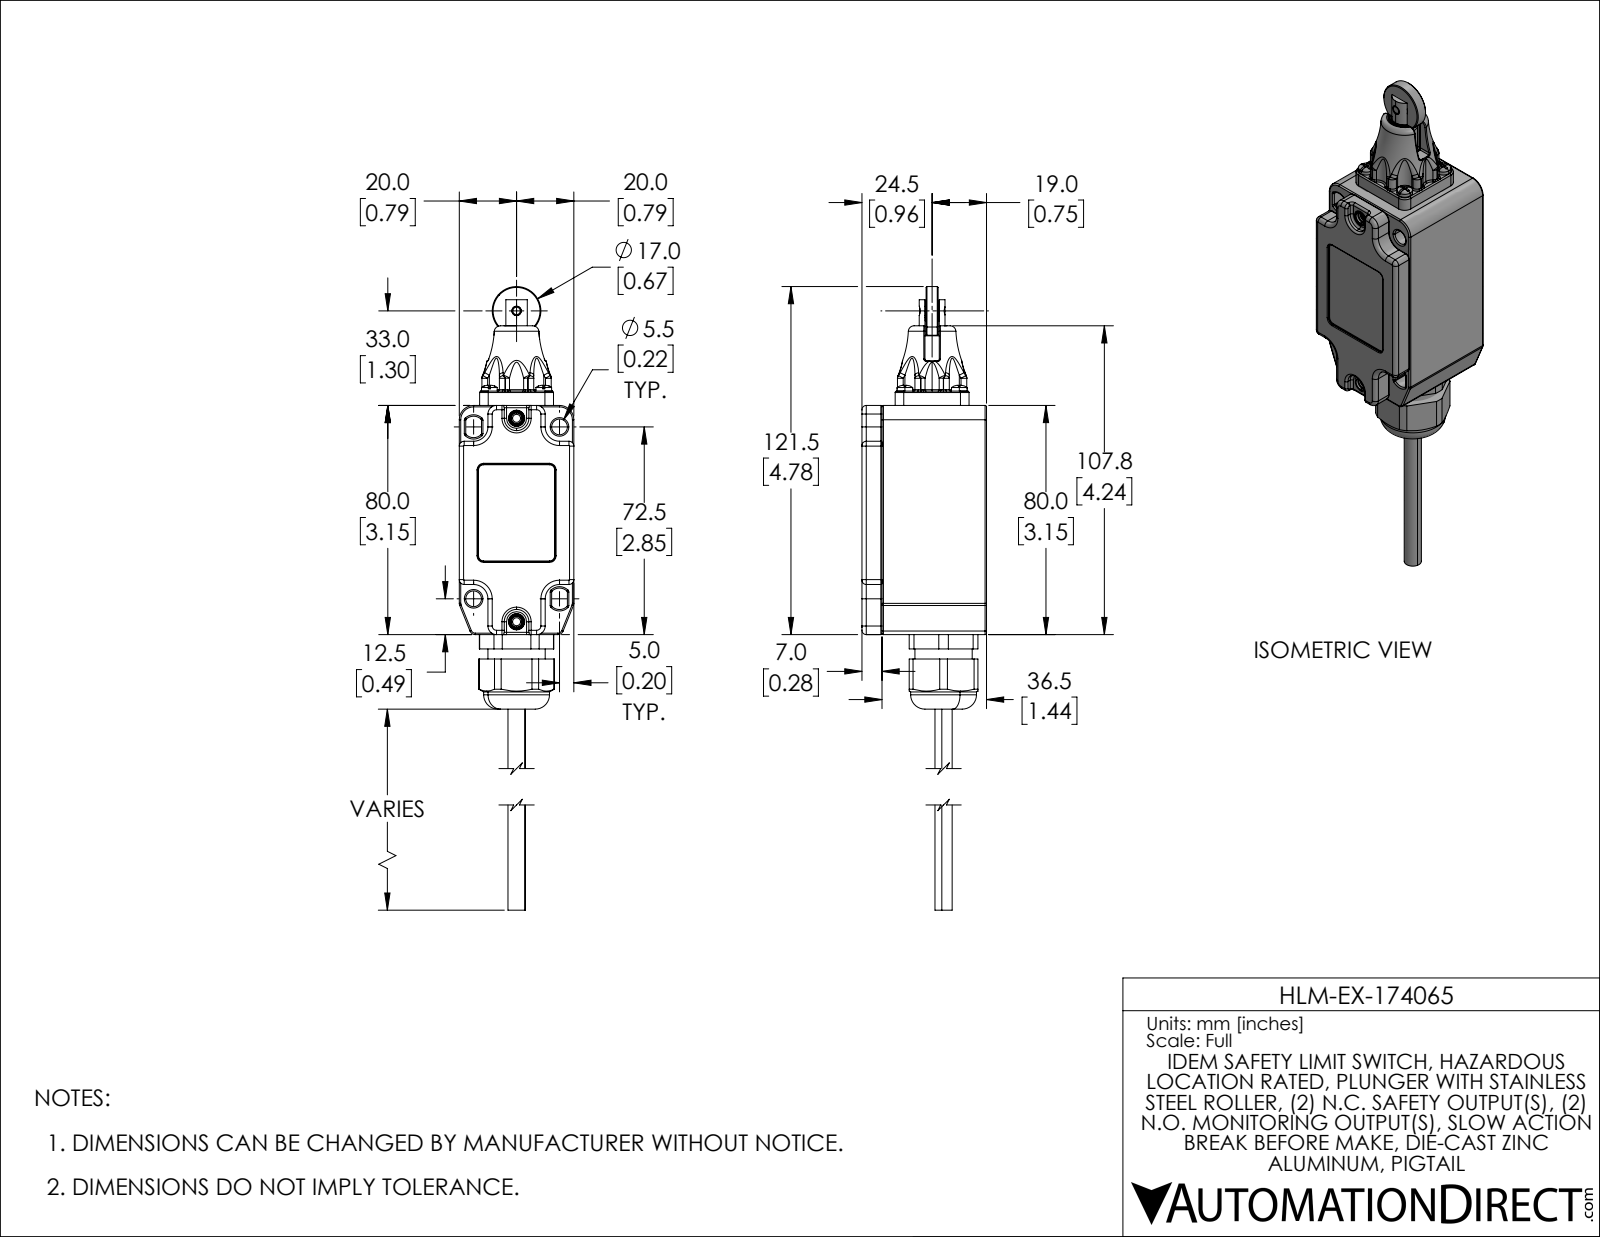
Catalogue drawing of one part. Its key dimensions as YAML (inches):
part_name: "HLM-EX-174065"
step_written_by: "SolidWorks 2021 (AUTOMOTIVE_DESIGN)"
units: inches
bodies: {solids: 14, faces: 2129, planar: 508, cylindrical: 586, other: 1035}
overall_size: [8.091, 1.713, 1.575]
volume: 4.536
surface_area: 79.67
round_holes:
  - {diameter: 0.118, count: 10}
  - {diameter: 0.13, count: 5}
  - {diameter: 0.146, count: 2}
  - {diameter: 0.15, count: 2}
  - {diameter: 0.157, count: 2}
  - {diameter: 0.165, count: 2}
  - {diameter: 0.217, count: 2}
  - {diameter: 0.492, count: 2}
  - {diameter: 0.059, count: 1}
  - {diameter: 0.098, count: 1}
  - {diameter: 0.138, count: 1}
  - {diameter: 0.173, count: 1}
round_bosses_or_shafts:
  - {diameter: 0.244, count: 6}
  - {diameter: 0.216, count: 4}
  - {diameter: 0.252, count: 2}
  - {diameter: 0.906, count: 1}
  - {diameter: 0.728, count: 1}
  - {diameter: 0.669, count: 1}
  - {diameter: 0.551, count: 1}
  - {diameter: 0.488, count: 1}
partial_cylinders:
  - {radius: 0.02, count: 169}
  - {radius: 0.016, count: 26}
  - {radius: 0.079, count: 24}
  - {radius: 0.006, count: 14}
  - {radius: 0.031, count: 12}
  - {radius: 0.008, count: 10}
  - {radius: 0.012, count: 10}
  - {radius: 0.039, count: 9}
face_to_face_distances: [0.089, 1.486, 1.575, 0.098, 1.398, 1.512, 0.102, 0.276, 1.61, 0.173]
hole_center_spacings: [0.748, 0.529, 0.354, 0.432, 0.65, 0.75, 0.828, 0.854]
